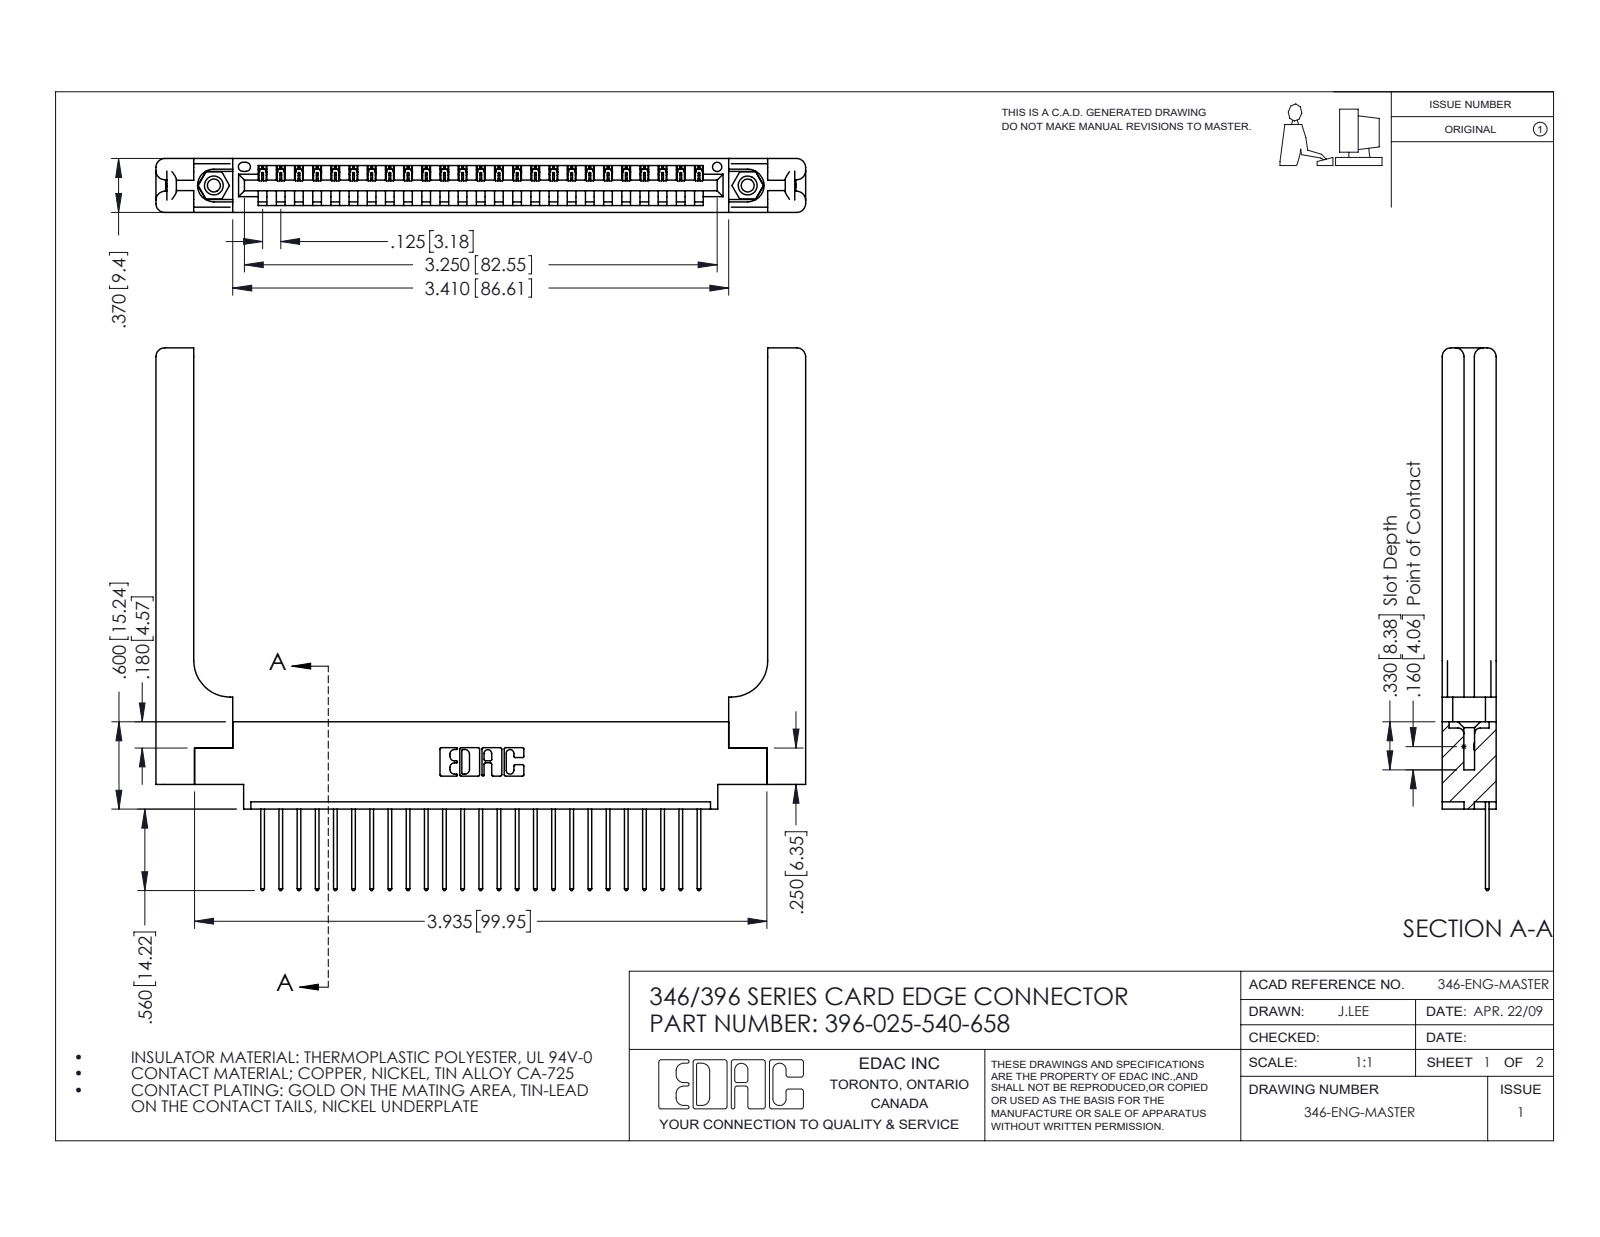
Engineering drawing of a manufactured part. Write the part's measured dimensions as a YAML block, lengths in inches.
part_name: "396-025-540-658; 345-250-001_345-250-001-102; 346 Part_0.170 Offset - 0.156 Dia-TH; 346-220-058_345-220-058 (+1 more)"
step_written_by: "SolidWorks 2016 (CONFIG_CONTROL_DESIGN)"
units: inches
bodies: {solids: 30, faces: 1832, planar: 1228, cylindrical: 544, other: 60}
overall_size: [4.466, 3.73, 0.37]
volume: 1.107
surface_area: 28.94
round_holes:
  - {diameter: 0.089, count: 2}
  - {diameter: 0.125, count: 2}
  - {diameter: 0.156, count: 2}
  - {diameter: 0.064, count: 1}
round_bosses_or_shafts:
  - {diameter: 0.155, count: 2}
partial_cylinders:
  - {radius: 0.006, count: 50}
  - {radius: 0.01, count: 50}
  - {radius: 0.01, count: 22}
  - {radius: 0.06, count: 16}
  - {radius: 0.007, count: 6}
  - {radius: 0.031, count: 6}
  - {radius: 0.026, count: 3}
  - {radius: 0.03, count: 2}
face_to_face_distances: [0.37, 0.072, 0.048, 0.322, 0.15, 0.148, 0.25, 0.298, 0.025, 0.077]
hole_center_spacings: [0.246, 3.462, 3.67]
